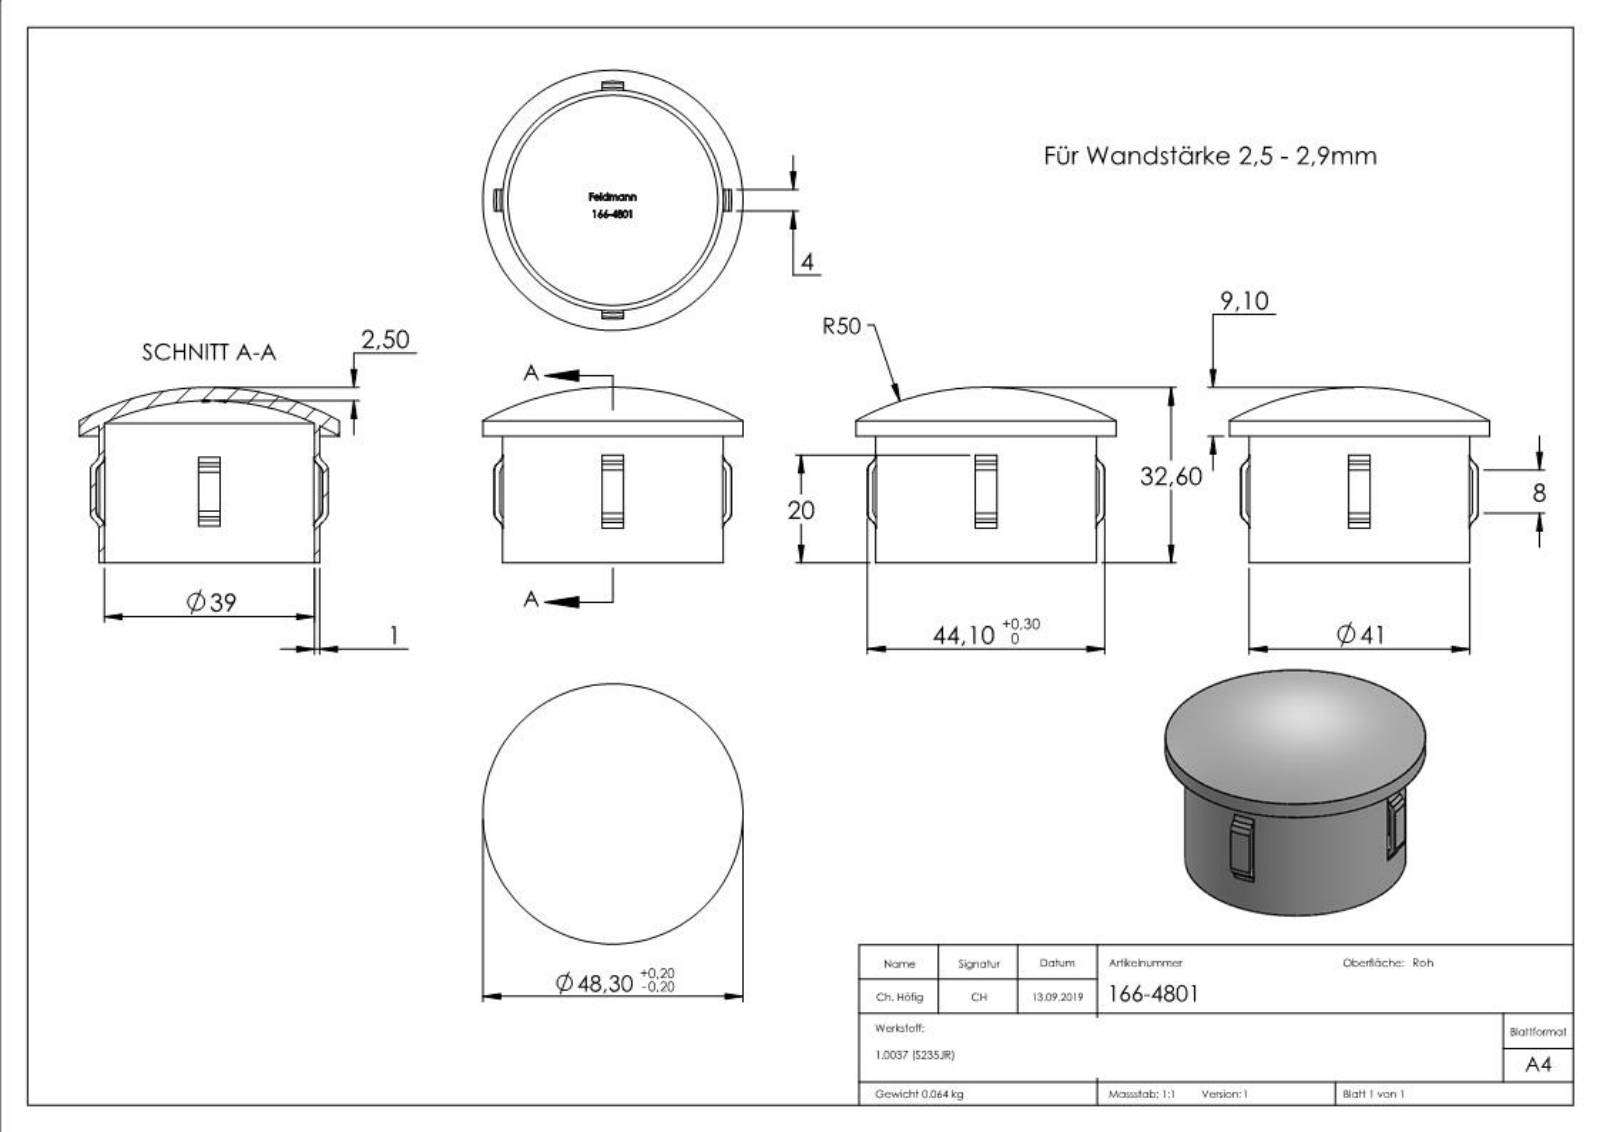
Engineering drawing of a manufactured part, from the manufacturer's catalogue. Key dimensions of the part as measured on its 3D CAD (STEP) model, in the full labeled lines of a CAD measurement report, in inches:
Part name (STEP PRODUCT): 166-4801
STEP written by: SolidWorks 2015 (CONFIG_CONTROL_DESIGN)
Units: inches
Bodies: 1 solid, 314 faces (106 planar, 16 cylindrical, 192 other)
Overall size (bounding box): 1.902 × 1.902 × 1.283
Volume: 0.497 in³ · Surface area: 17.08 in²
Round holes (diameter × count): ⌀1.535 ×1
Round bosses / shafts (diameter × count): ⌀1.902 ×1, ⌀1.614 ×1
Partial cylindrical surfaces — rounded edges, fillets, slot ends (radius × count): R0.829 ×1, R0.868 ×1
Main face-to-face distances: 0.157, 0.079, 0.153, 0.05, 0.265, 0.056, 0.117, 0.129, 0.112, 0.034
